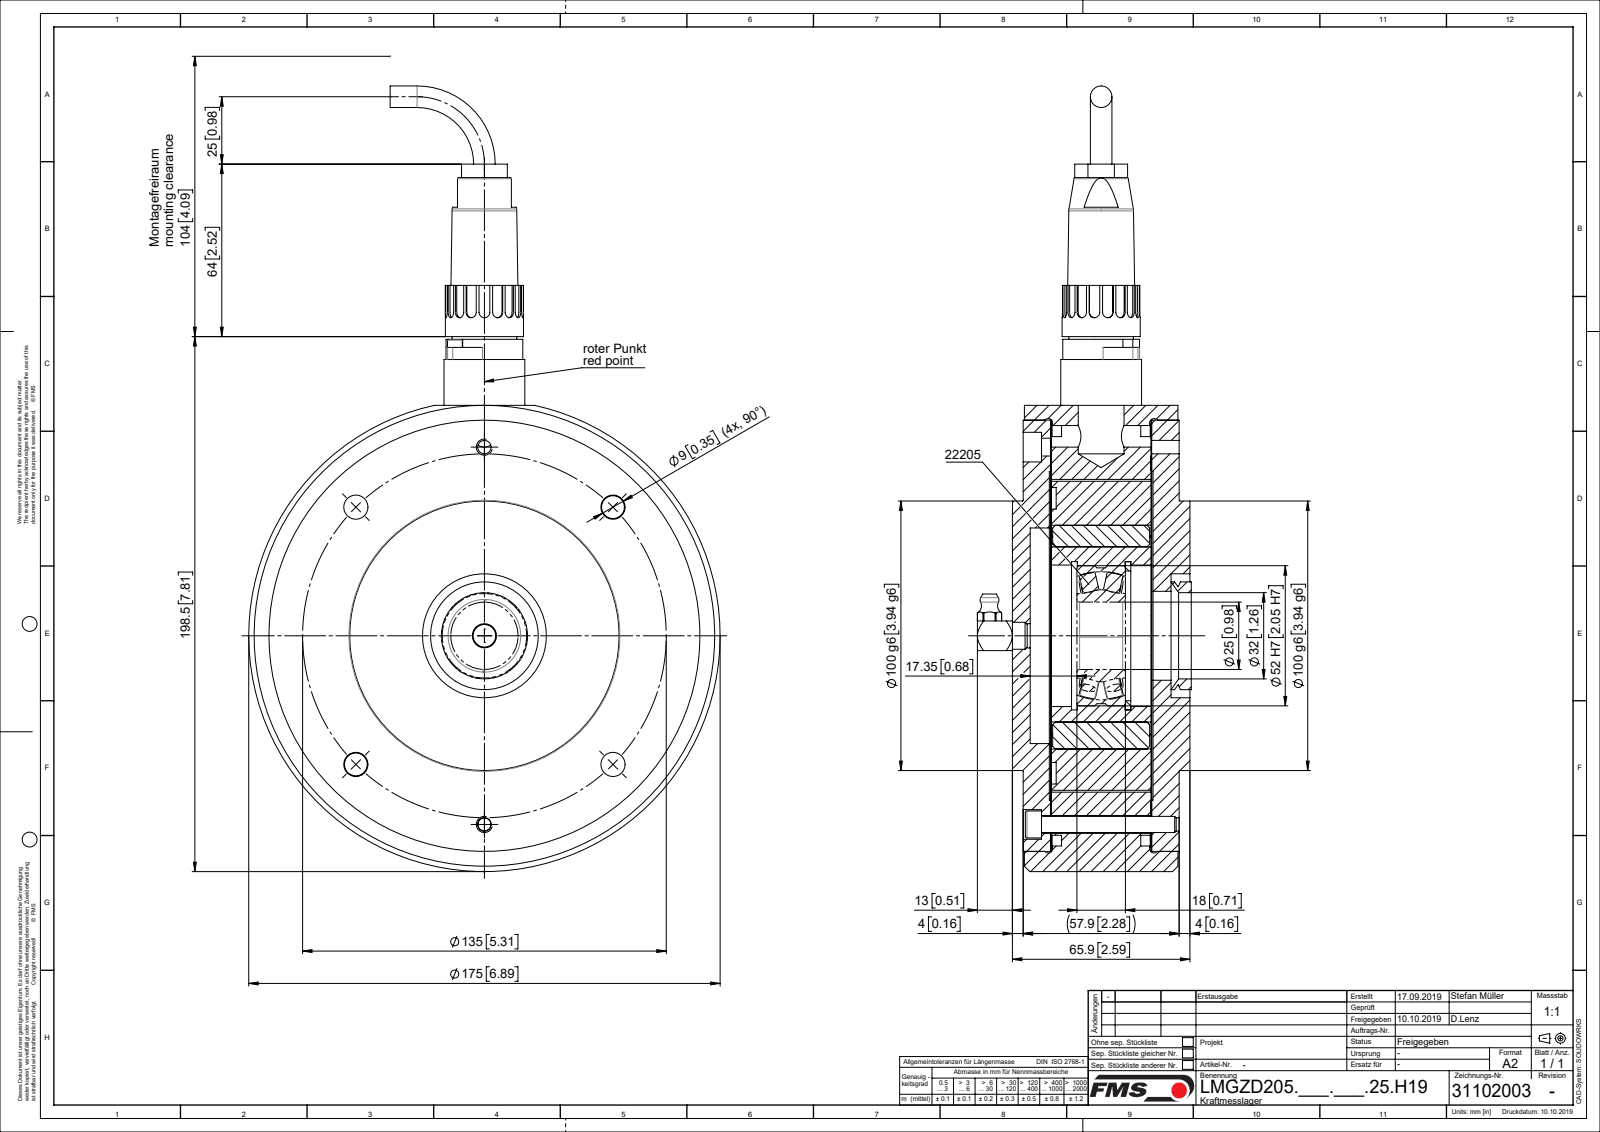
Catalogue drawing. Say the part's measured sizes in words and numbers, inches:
The part is named "Zyl-Schr DIN912_M3x25; PRL_22205_01; 49960_01; 49024_01 (+8 more)". Its 3-D file was written by "SolidWorks 2018 (CONFIG_CONTROL_DESIGN)". It is 51 solids with 862 faces: 229 planar, 343 cylindrical and 290 other. Overall it measures 11.476 by 6.89 by 3.126 inches. Its volume is 81.47 cubic inches and its surface area 437.1 square inches. Round holes: 6 of diameter 0.098, 5 of diameter 0.354, 3 of diameter 0.126, 2 of diameter 0.134, 2 of diameter 0.142, 2 of diameter 0.197, 2 of diameter 0.26, 2 of diameter 0.315, 2 of diameter 0.335, 2 of diameter 0.433, 1 of diameter 0.394, 1 of diameter 0.413. Round bosses or shafts: 7 of diameter 0.085, 2 of diameter 0.394, 2 of diameter 0.217, 2 of diameter 0.118, 1 of diameter 6.89, 1 of diameter 6.299, 1 of diameter 5.827, 1 of diameter 3.937. Partial cylindrical surfaces (rounded edges, fillets, slot ends): 19 of radius 0.079, 4 of radius 0.004, 2 of radius 0.118, 2 of radius 0.167, 2 of radius 0.295, 2 of radius 0.354, 2 of radius 0.433, 1 of radius 0.177. The main face-to-face distances are 1.467, 0.402, 0.411, 1.868, 1.878, 1.457, 1.476, 1.496, 0.03, 0.382. The hole center spacings are 0.64, 0.885, 0.906, 1.926, 2.074, 2.657, 3.758, 3.829.
